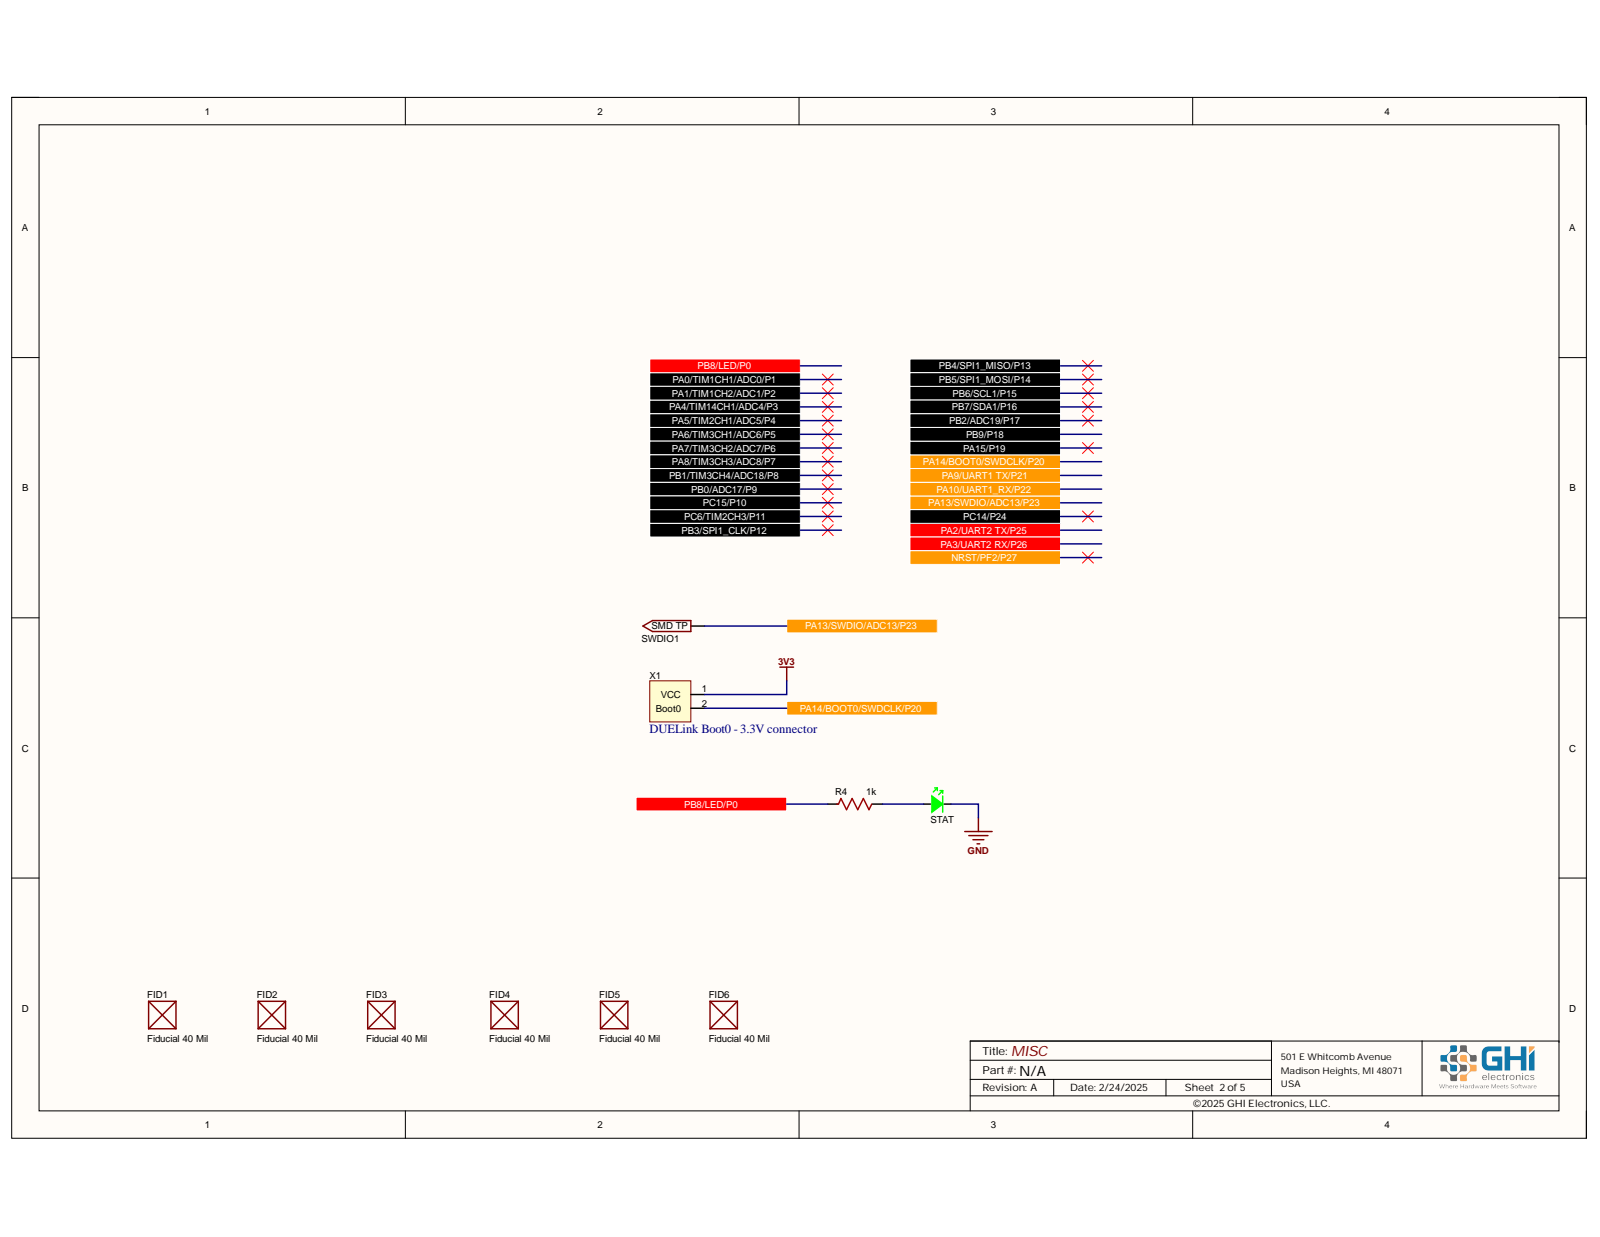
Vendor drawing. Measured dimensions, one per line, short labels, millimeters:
name: PCB; Board; U; DUELink-Connector-BM04B-SRSS-TB (+5 more)
written by: Open CASCADE 7.5 (AUTOMOTIVE_DESIGN)
unit: mm
bodies: 99 solids, 2191 faces (1407 planar, 504 cylindrical, 280 other)
size: 35.54 × 27 × 13.49
volume: 2 785 mm³; area: 4 268 mm²
holes: 4× ⌀0.89, 2× ⌀1.02, 2× ⌀3, 1× ⌀2.6
bosses: 3× ⌀0.4
rounds: 135× R0.1, 35× R0.12, 14× R0.15, 8× R0.2, 6× R0.25, 3× R0.5, 2× R0.17, 2× R0.18
face distances: 1.6, 2.24, 3.84, 1.3, 11.64, 5.54, 4.5, 3.2, 10.34, 10.04
hole spacings: 2, 4, 5.46, 8.06, 9.85, 11.7, 13.6, 14.74
